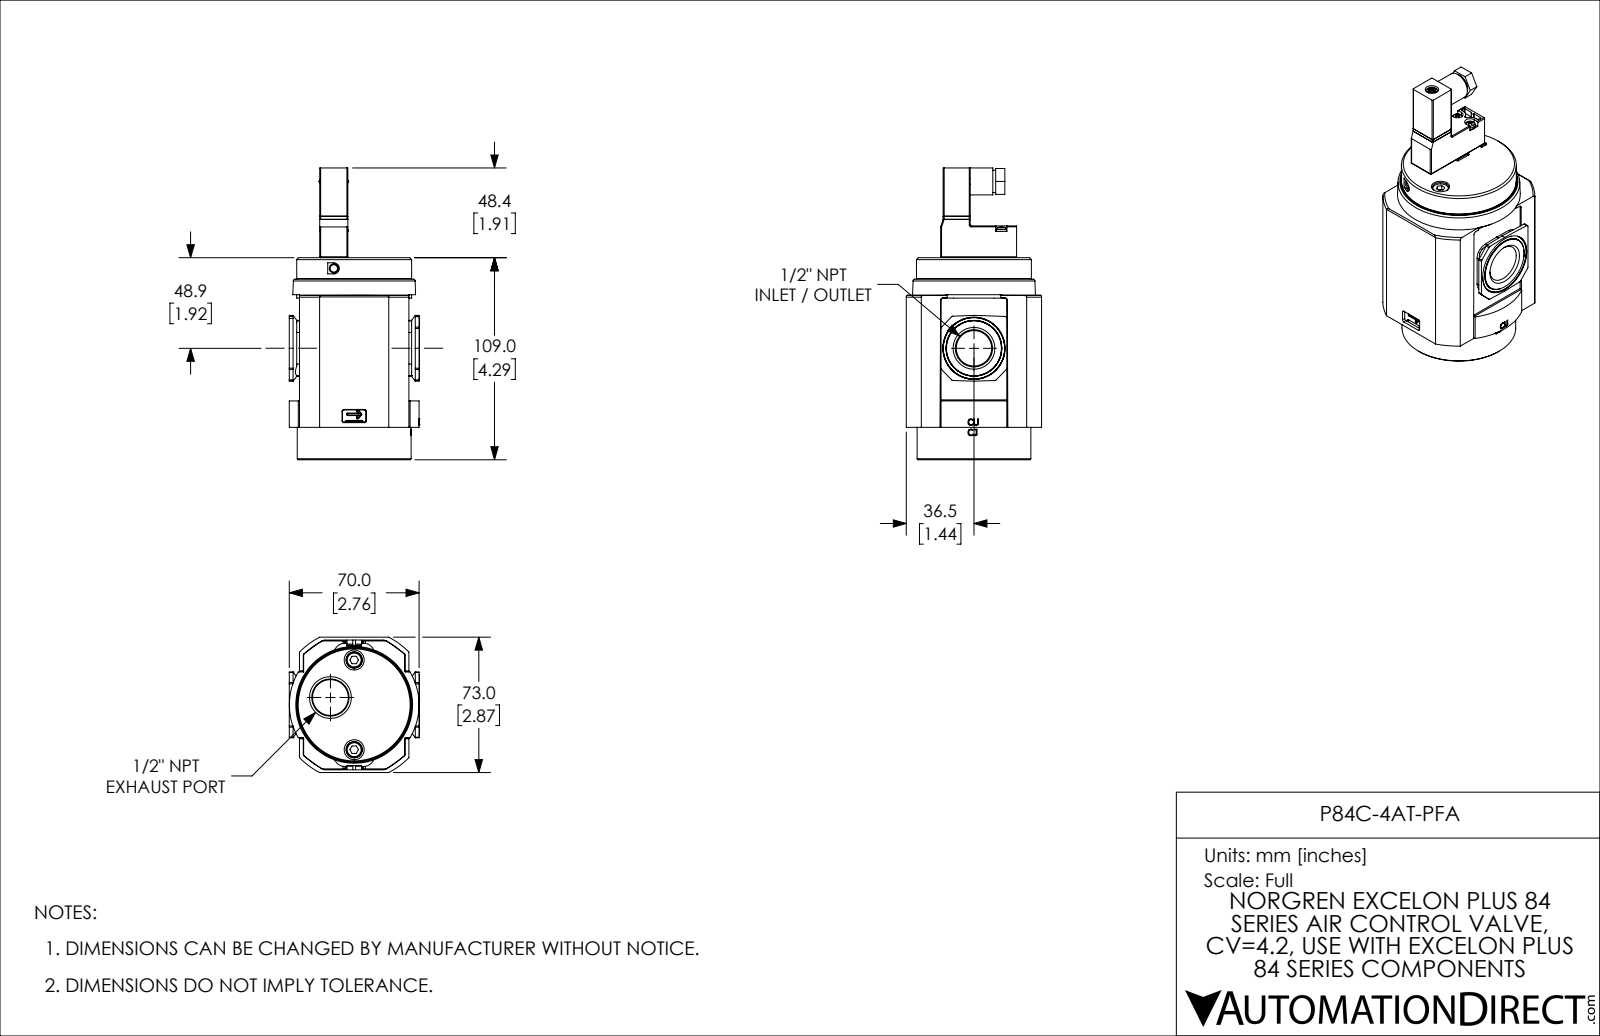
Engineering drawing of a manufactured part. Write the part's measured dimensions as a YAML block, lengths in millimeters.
part_name: "P84C-4AT-PFA"
step_written_by: "SolidWorks 2021 (CONFIG_CONTROL_DESIGN)"
units: millimeters
bodies: {solids: 7, faces: 843, planar: 396, cylindrical: 250, other: 197}
overall_size: [157.35, 73, 70.25]
volume: 420399
surface_area: 95846
round_holes:
  - {diameter: 4.92, count: 4}
  - {diameter: 5.3, count: 4}
  - {diameter: 8.8, count: 4}
  - {diameter: 1.5, count: 3}
  - {diameter: 2.46, count: 3}
  - {diameter: 0.8, count: 2}
  - {diameter: 3.1, count: 2}
  - {diameter: 8.5, count: 2}
  - {diameter: 3.8, count: 1}
  - {diameter: 6.8, count: 1}
  - {diameter: 7.2, count: 1}
round_bosses_or_shafts:
  - {diameter: 8.5, count: 4}
  - {diameter: 5, count: 4}
  - {diameter: 3, count: 2}
  - {diameter: 62, count: 1}
  - {diameter: 61.4, count: 1}
  - {diameter: 59, count: 1}
  - {diameter: 14.5, count: 1}
  - {diameter: 12, count: 1}
partial_cylinders:
  - {radius: 0.5, count: 25}
  - {radius: 0.25, count: 14}
  - {radius: 1, count: 13}
  - {radius: 3, count: 4}
  - {radius: 6, count: 4}
  - {radius: 6.3, count: 4}
  - {radius: 0.55, count: 2}
  - {radius: 0.94, count: 2}
face_to_face_distances: [1.5, 70.2, 2, 71, 71.5, 69.5, 0.5, 11.25, 70, 81.45]
hole_center_spacings: [3.8, 5.05, 5.41, 7.11, 12.41, 24.88, 46.75, 1.41]
